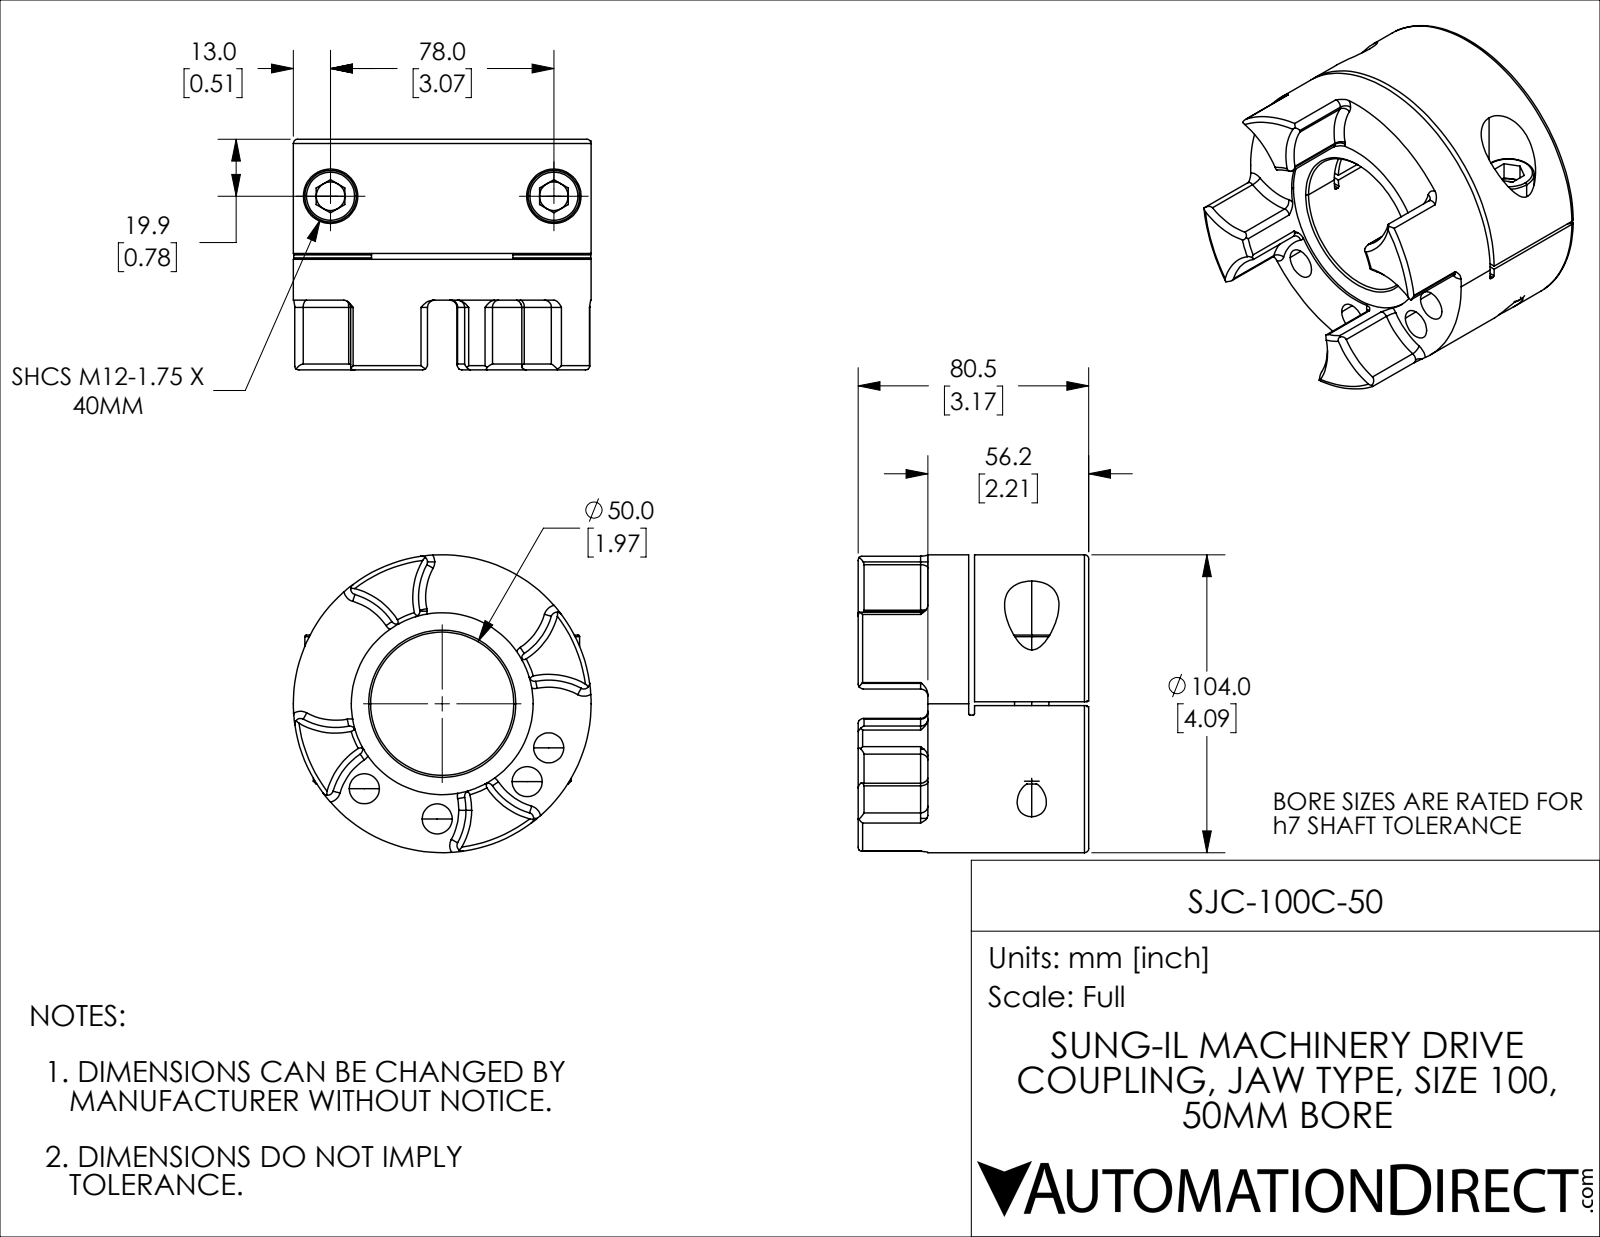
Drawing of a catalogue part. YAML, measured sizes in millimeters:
part_name: "SJC-100C-50"
step_written_by: "SolidWorks 2021 (CONFIG_CONTROL_DESIGN)"
units: millimeters
bodies: {solids: 4, faces: 222, planar: 55, cylindrical: 82, other: 85}
overall_size: [104, 104, 80.5]
volume: 376454
surface_area: 70468
round_holes:
  - {diameter: 10.5, count: 4}
  - {diameter: 10, count: 2}
  - {diameter: 10.2, count: 2}
  - {diameter: 12.5, count: 2}
  - {diameter: 19, count: 2}
  - {diameter: 50, count: 1}
  - {diameter: 63.5, count: 1}
round_bosses_or_shafts:
  - {diameter: 18, count: 2}
  - {diameter: 12, count: 2}
  - {diameter: 104, count: 1}
partial_cylinders:
  - {radius: 2, count: 16}
  - {radius: 23.68, count: 4}
  - {radius: 0.5, count: 2}
  - {radius: 75, count: 1}
face_to_face_distances: [2, 41.9, 39.9, 56.2, 16.3, 14.3, 55.3, 15.4, 13.4, 0.9]
hole_center_spacings: [40.25, 13.98, 27.52, 34.03, 46.18, 56.92, 65.94, 78]
